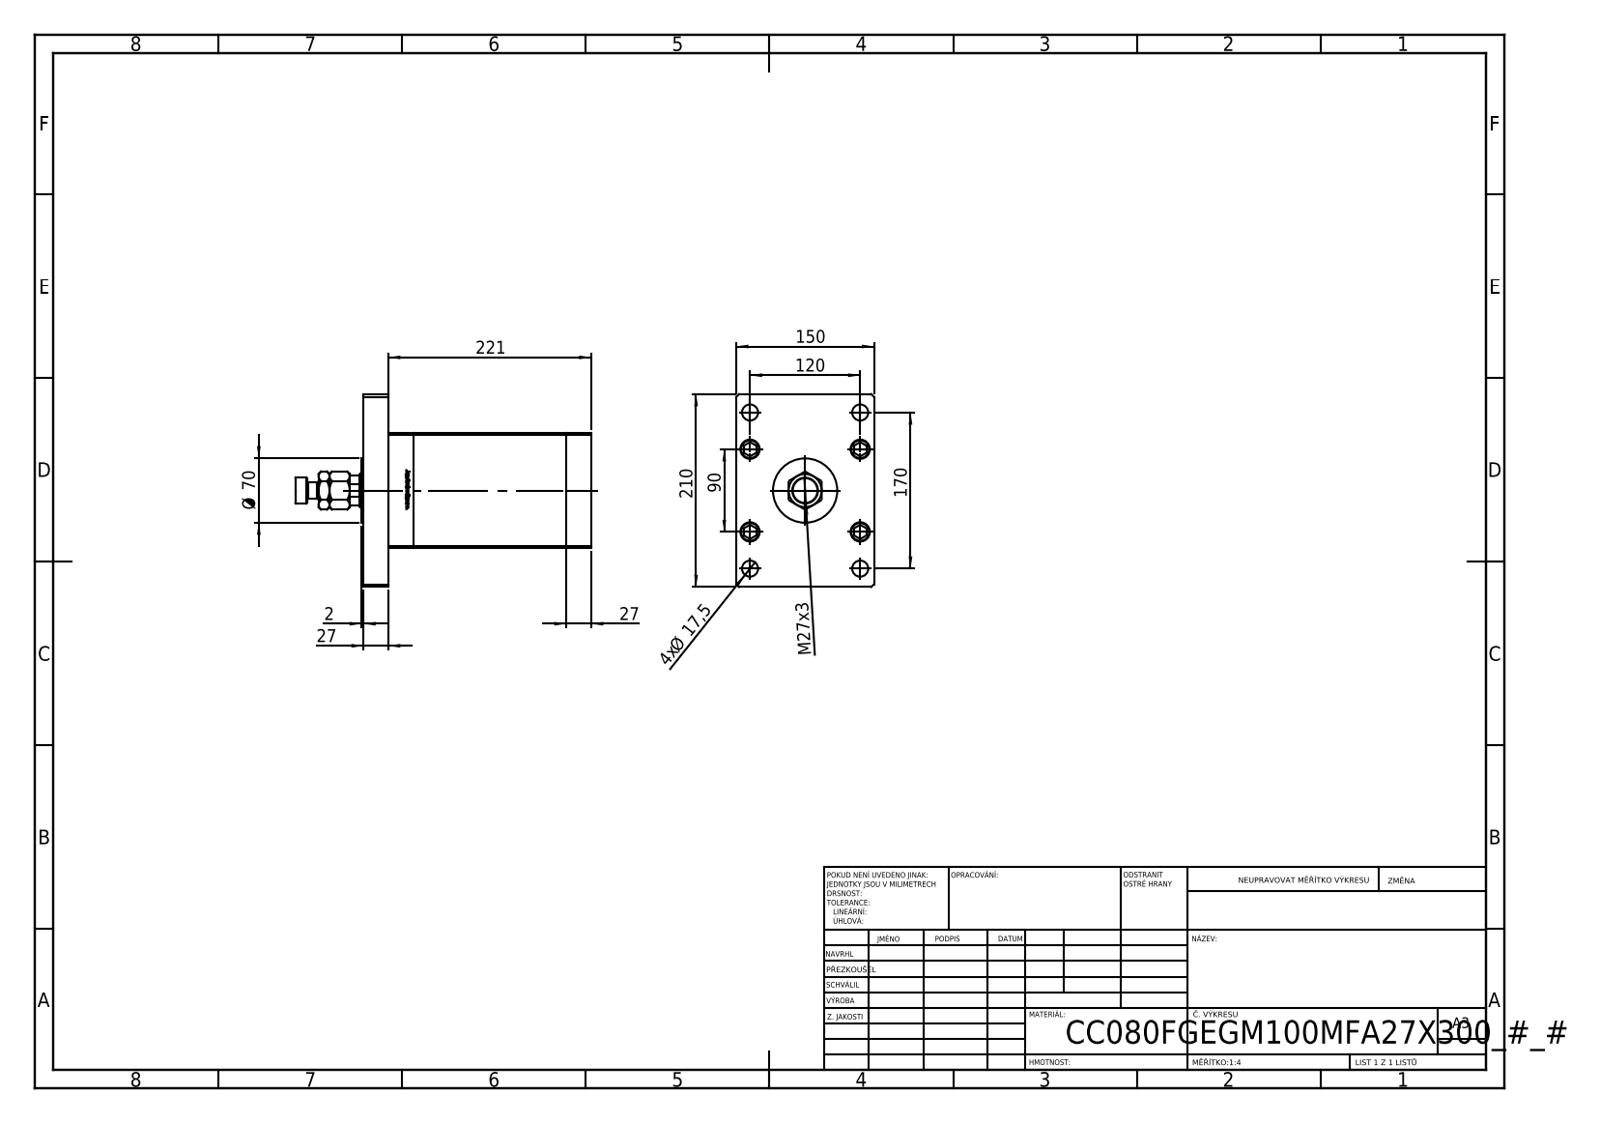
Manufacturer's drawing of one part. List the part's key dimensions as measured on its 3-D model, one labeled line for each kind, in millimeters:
Part name (STEP PRODUCT): V220C BACK_F; V220C_VC_F; V220C_F; MFA (+3 more)
STEP written by: SolidWorks 2019 (CONFIG_CONTROL_DESIGN)
Units: millimetres
Bodies: 20 solids, 1362 faces (533 planar, 191 cylindrical, 638 other)
Overall size (bounding box): 322 × 210 × 150
Volume: 4 412 000 mm³ · Surface area: 480 880 mm²
Round holes (diameter × count): ⌀17.5 ×9, ⌀22 ×5, ⌀16 ×4, ⌀21 ×4, ⌀2 ×2, ⌀13.16 ×2, ⌀25.5 ×1, ⌀36 ×1, ⌀37.5 ×1
Round bosses / shafts (diameter × count): ⌀8 ×9, ⌀21 ×5, ⌀80 ×1, ⌀70 ×1, ⌀28 ×1, ⌀18 ×1
Partial cylindrical surfaces — rounded edges, fillets, slot ends (radius × count): R0.93 ×2, R17.5 ×1
Main face-to-face distances: 27, 194, 221, 150, 125, 167, 54, 248, 33.5, 6.5
Hole centre spacings: 51, 40, 75, 104.04, 120, 126.49, 130, 176.92
